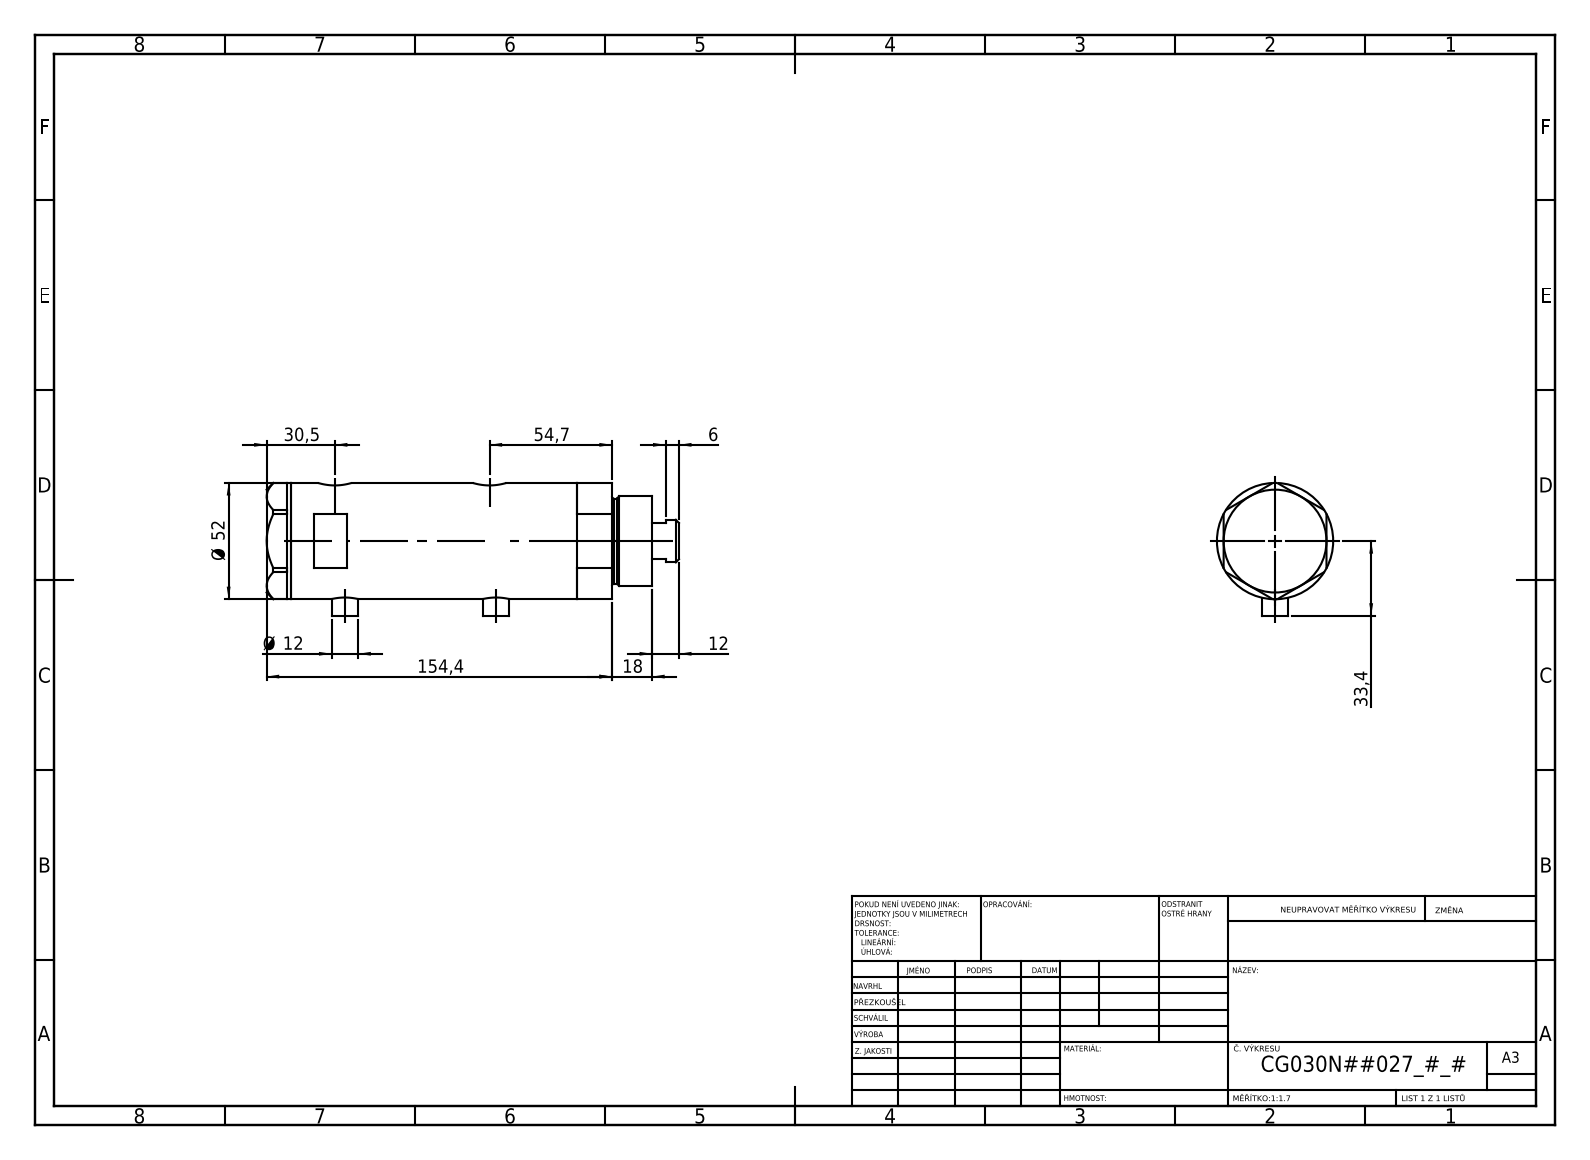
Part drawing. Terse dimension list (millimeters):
name: V270CG_BACK; V270CG_VC; V270CG_FRONT; V270CG_MIDDLE
written by: SolidWorks 2019 (CONFIG_CONTROL_DESIGN)
unit: mm
bodies: 4 solids, 134 faces (65 planar, 49 cylindrical, 20 other)
size: 184.4 × 59.4 × 52
volume: 336 098 mm³; area: 77 229 mm²
holes: 2× ⌀9.73, 2× ⌀12.5, 2× ⌀15, 1× ⌀6.5, 1× ⌀20, 1× ⌀21.5, 1× ⌀30, 1× ⌀33, 1× ⌀44
bosses: 2× ⌀12, 1× ⌀52, 1× ⌀40, 1× ⌀38, 1× ⌀19
face distances: 91.5, 23.8, 67.7, 11, 34.8, 102.5, 46, 138.9, 127.9, 104.1
hole spacings: 2.9, 4.5, 64.7, 67.6, 69.2, 72.1
